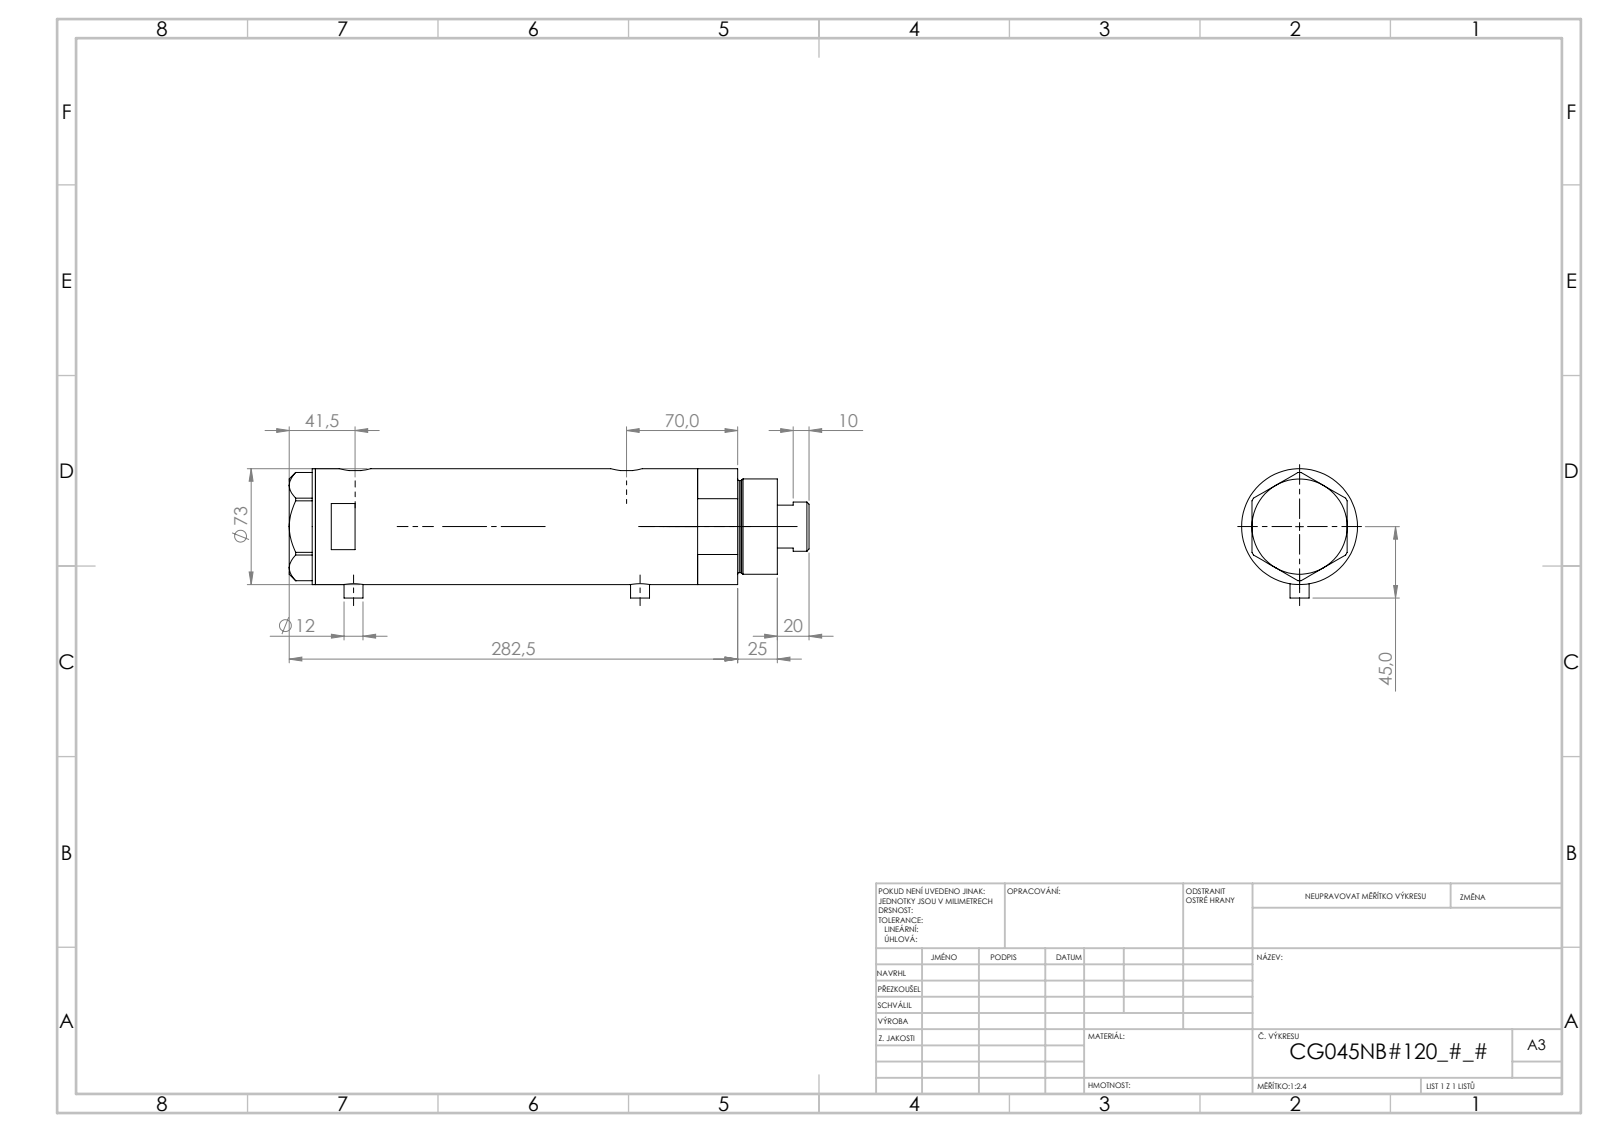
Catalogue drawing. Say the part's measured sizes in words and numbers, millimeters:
The part is named "V270CG_FRONT; V270CG_MIDDLE; V270CG_VC; V270CG_BACK". Its 3-D file was written by "SolidWorks 2019 (CONFIG_CONTROL_DESIGN)". It is 4 solids with 125 faces: 50 planar, 55 cylindrical and 20 other. Overall it measures 311.52 by 74.1 by 73 millimeters. Its volume is 1 075 000 cubic millimeters and its surface area 176 489 square millimeters. Round holes: 2 of diameter 5, 2 of diameter 12.5, 2 of diameter 13.16, 1 of diameter 10.5, 1 of diameter 32, 1 of diameter 33.5, 1 of diameter 45, 1 of diameter 48, 1 of diameter 64. Round bosses or shafts: 2 of diameter 12, 1 of diameter 73, 1 of diameter 60, 1 of diameter 58, 1 of diameter 31. Partial cylindrical surfaces (rounded edges, fillets, slot ends): 2 of radius 10. The main face-to-face distances are 187.14, 26, 161.14, 16.5, 42.5, 203.64, 275.01, 291.51, 249.01, 87.87. The hole center spacings are 171.65, 0.99, 1, 8.5, 8.51, 162.15, 163.14, 163.15.
